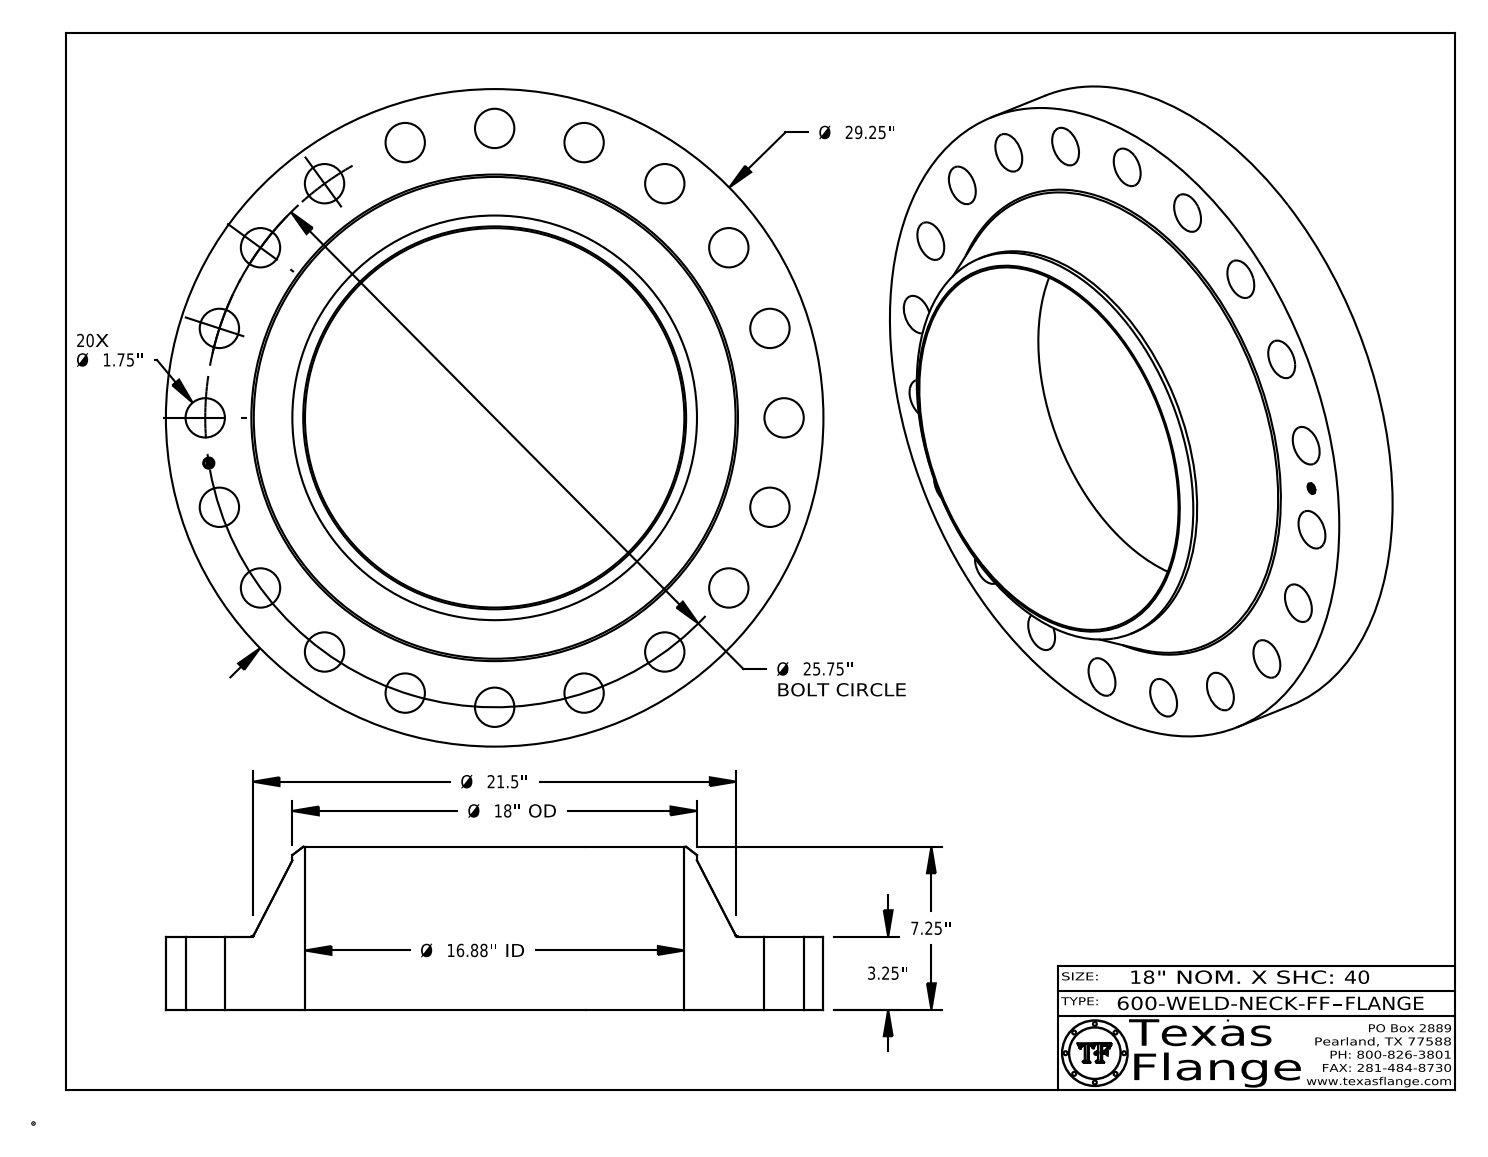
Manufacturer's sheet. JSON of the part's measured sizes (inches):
{"part_name": "600-WELD-NECK-FF", "step_written_by": "CATIA V5 STEP AP214 (AUTOMOTIVE_DESIGN)", "units": "inches", "bodies": {"solids": 1, "faces": 440, "planar": 368, "cylindrical": 66, "other": 6}, "overall_size": [29.25, 29.25, 7.25], "volume_in3": 1598, "surface_area_in2": 1988, "round_holes": [[1.75, 20], [0.495, 1], [16.876, 1]], "round_bosses_or_shafts": [[0.03, 8], [29.25, 1], [18, 1], [0.39, 1]], "face_to_face_distances": [3.25, 7.25, 4, 0.015, 3.235, 4.015, 0.148, 0.145, 0.027, 0.096], "hole_center_spacings": [12.875, 24.49, 25.433, 7.957, 11.691, 4.028, 15.135, 18.208]}
